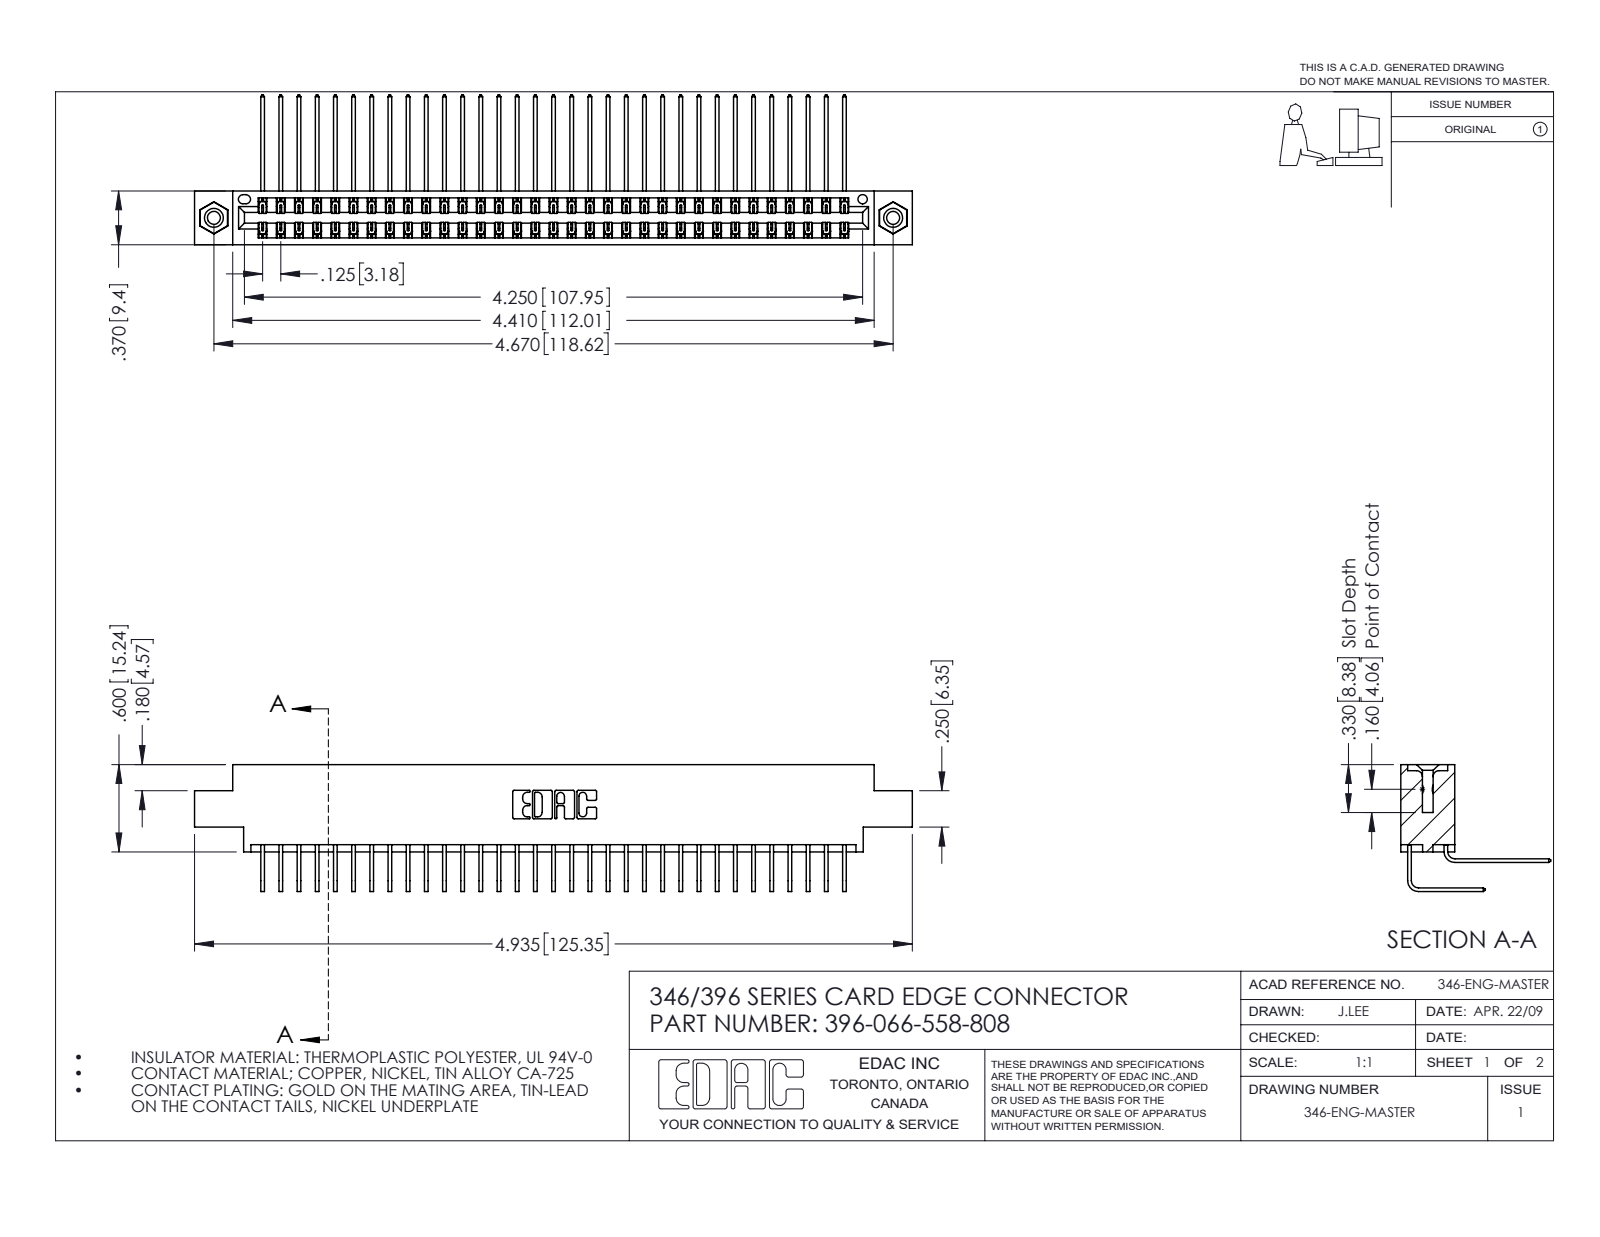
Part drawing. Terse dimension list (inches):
name: 345-292-001_558 Tail - 2; 346 Part_0.170 Offset - 0.156 Dia-TI; 345-292-001_558 559 Tail - 1; 345-250-001_345-250-003-102 (+1 more)
written by: SolidWorks 2016 (CONFIG_CONTROL_DESIGN)
unit: in
bodies: 69 solids, 3750 faces (2554 planar, 1180 cylindrical, 16 other)
size: 4.935 × 1.03 × 0.873
volume: 0.755 in³; area: 29.28 in²
holes: 2× ⌀0.089, 2× ⌀0.125, 2× ⌀0.156, 1× ⌀0.064
bosses: 2× ⌀0.155
rounds: 99× R0.006, 22× R0.01, 6× R0.007, 6× R0.031, 3× R0.026, 2× R0.014, 2× R0.022, 2× R0.024
face distances: 0.322, 0.048, 0.025, 0.37, 0.25, 0.298, 0.072, 0.275, 0.222, 0.148
hole spacings: 0.246, 4.462, 4.67
